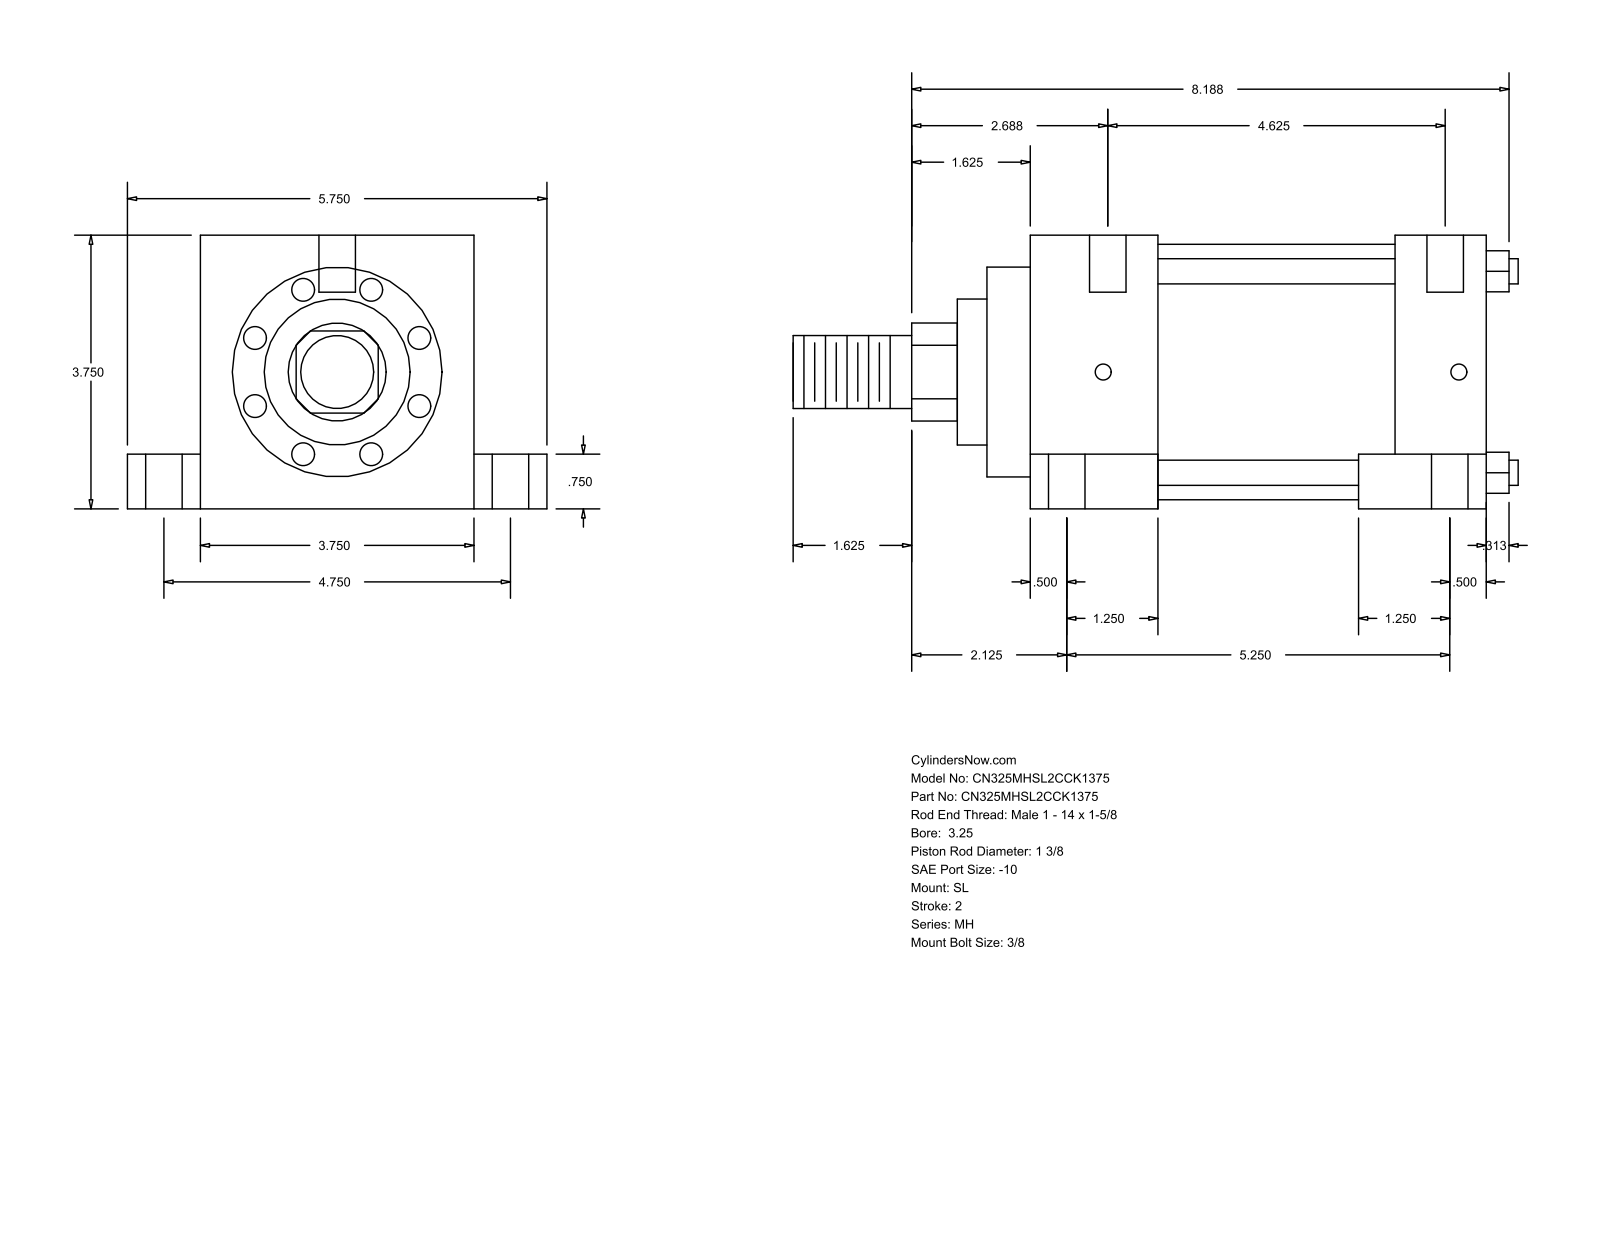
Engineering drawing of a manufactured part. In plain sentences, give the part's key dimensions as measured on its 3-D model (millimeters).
The part is named "MH_SL__0325_1.375". Its 3-D file was written by "GSSL Pune (CONFIG_CONTROL_DESIGN)". It is 0 solids with 110 faces: 77 planar, 33 cylindrical and 0 other. Overall it measures 252.41 by 146.05 by 95.25 millimeters. Round holes: 6 of diameter 12.7, 4 of diameter 5.56, 4 of diameter 19.05. Round bosses or shafts: 4 of diameter 8.76, 1 of diameter 88.9, 1 of diameter 73.03, 1 of diameter 50.8, 1 of diameter 34.92, 1 of diameter 25.4. Partial cylindrical surfaces (rounded edges, fillets, slot ends): 1 of radius 17.06. The main face-to-face distances are 95.24, 158.76, 44.45, 114.31, 25.41, 120.65, 19.05, 76.19, 127.01, 82.56. The hole center spacings are 60.35, 60.41, 61.65, 62, 120.66, 123.83, 133.34, 133.47.
